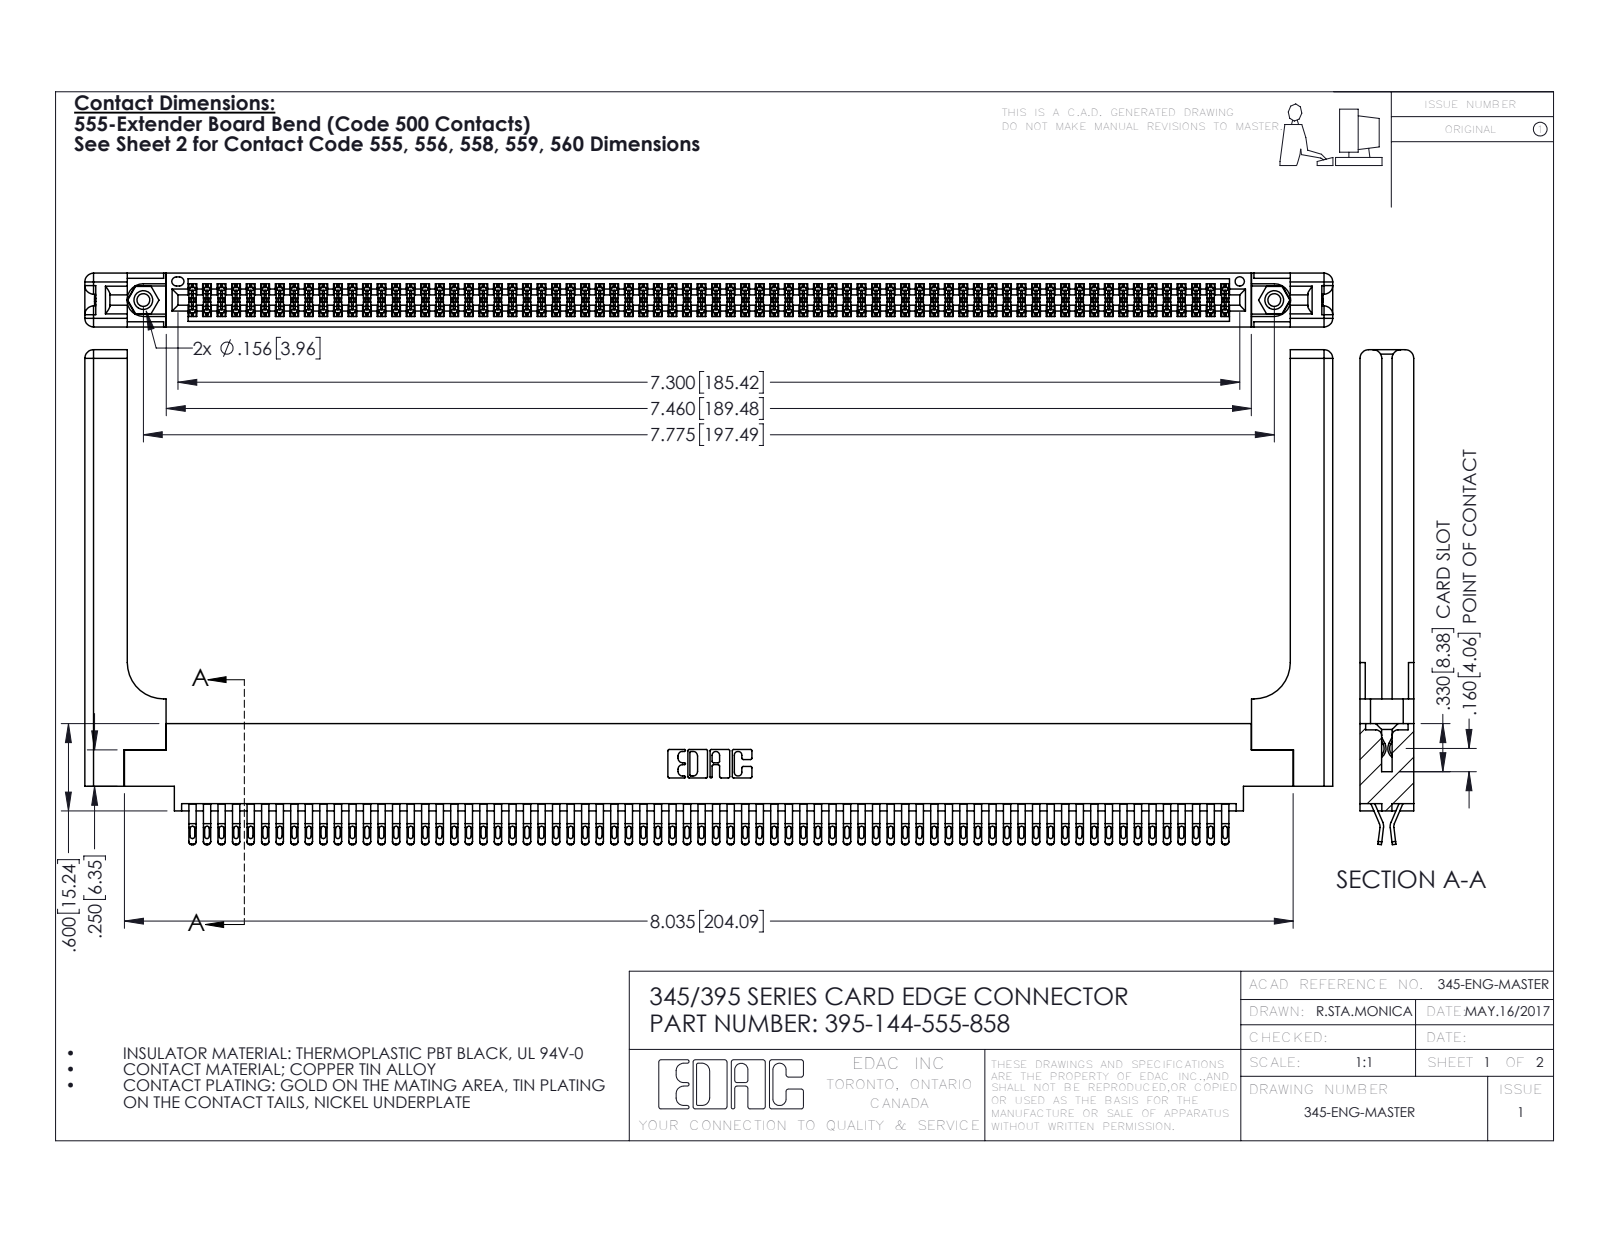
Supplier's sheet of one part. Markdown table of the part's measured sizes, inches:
| quantity | value |
| --- | --- |
| part name | 345-250-001_345-250-001-102; 345-220-058_345-220-058; 395-144-555-858; 345-292-001_555 Tail (+1 more) |
| STEP written by | SolidWorks 2016 (CONFIG_CONTROL_DESIGN) |
| units | inches |
| bodies | 149 solids, 8450 faces (4696 planar, 3694 cylindrical, 60 other) |
| overall size | 8.579 × 3.402 × 0.37 |
| volume | 1.844 in³ |
| surface area | 61.05 in² |
| round holes (diameter × count) | 0.089 × 2, 0.125 × 2, 0.156 × 2, 0.064 × 1 |
| round bosses / shafts (diameter × count) | 0.155 × 2 |
| partial cylindrical surfaces (radius × count) | 0.016 × 360, 0.02 × 288, 0.006 × 216, 0.01 × 22, 0.06 × 16, 0.007 × 6, 0.031 × 6, 0.026 × 3 |
| main face-to-face distances | 0.072, 0.298, 0.37, 0.025, 0.098, 0.272, 0.2, 0.225, 0.175, 0.148 |
| hole center spacings | 0.27, 7.539, 7.775 |
